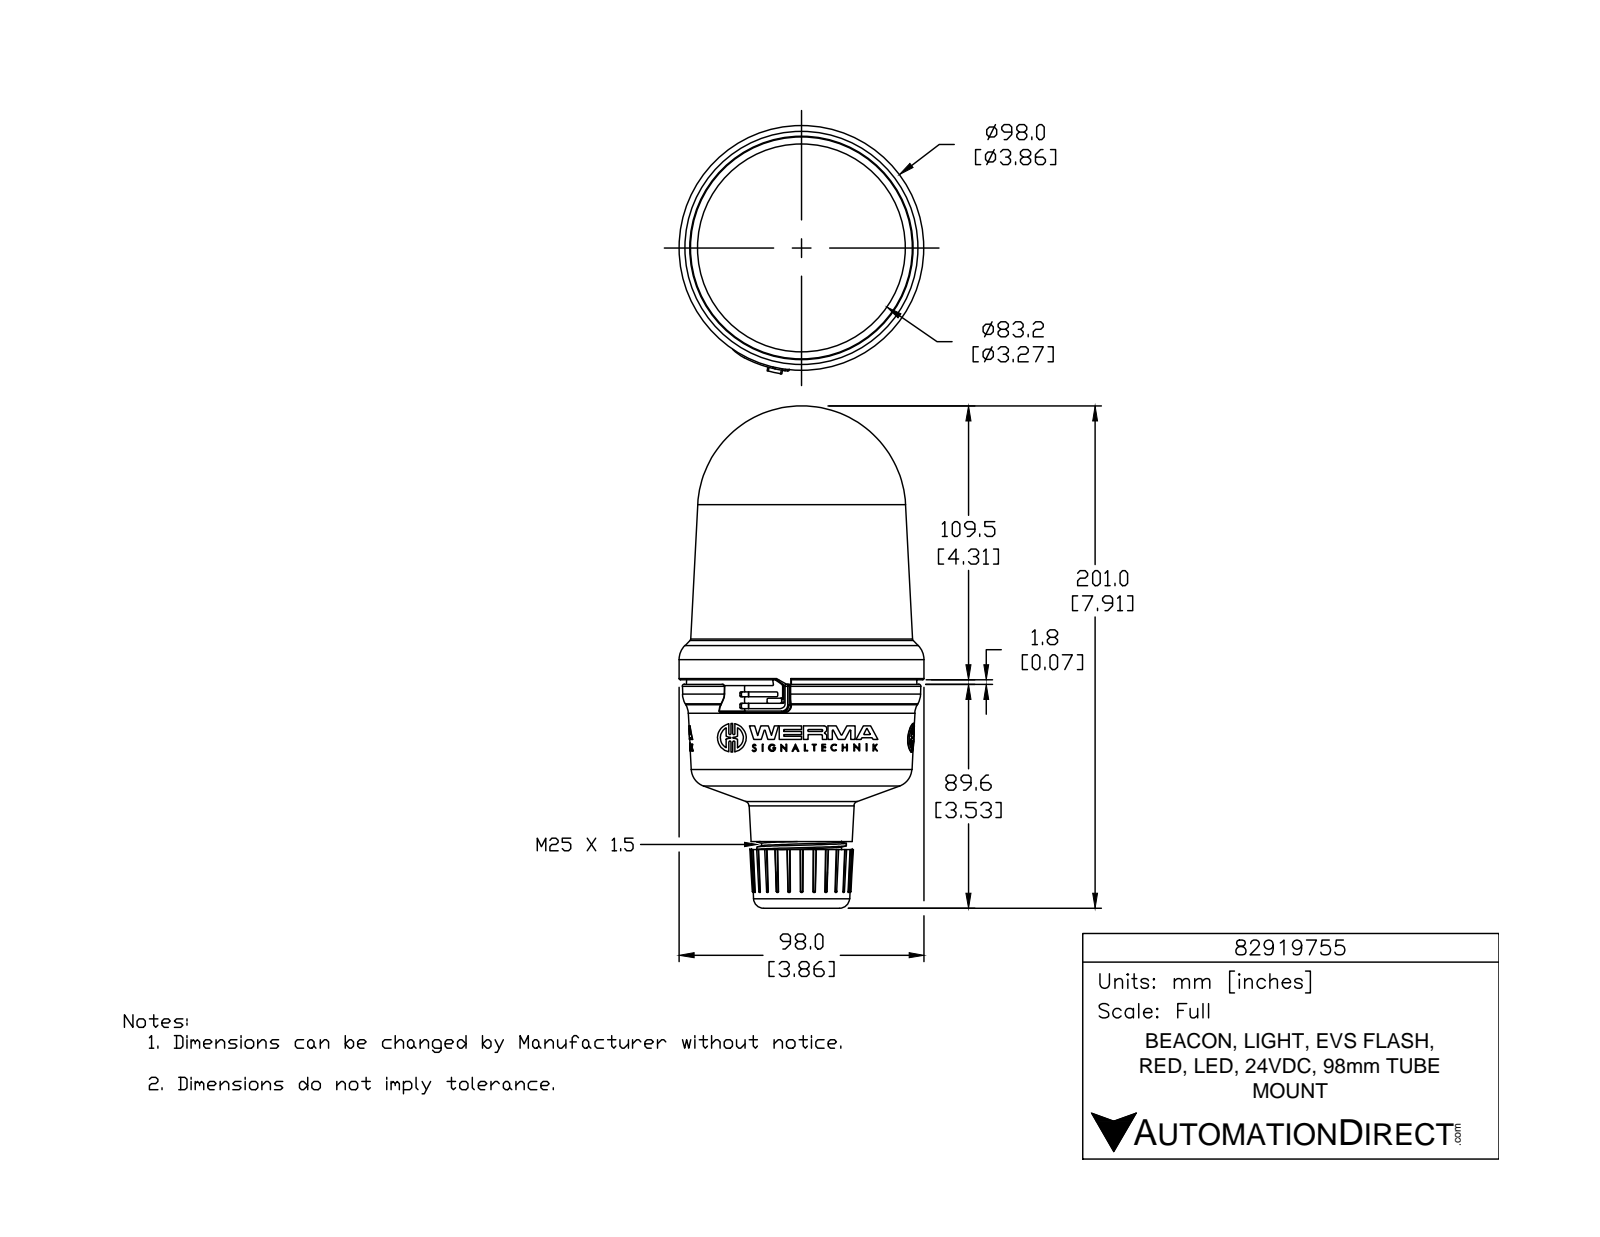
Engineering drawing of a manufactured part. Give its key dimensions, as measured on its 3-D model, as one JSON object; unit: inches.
{"part_name": "82919755", "step_written_by": "SolidWorks 2015 (AUTOMOTIVE_DESIGN)", "units": "inches", "bodies": {"solids": 1, "faces": 1006, "planar": 554, "cylindrical": 189, "other": 263}, "overall_size": [7.914, 3.912, 3.858], "volume_in3": 54.7, "surface_area_in2": 91.39, "round_holes": [[0.078, 3], [1.013, 1], [1.024, 1]], "round_bosses_or_shafts": [[0.452, 3], [0.113, 3], [3.858, 1], [1.409, 1], [1.261, 1]], "partial_cylinders_radius": [[0.02, 12], [0.007, 9], [0.007, 6], [0.016, 6], [0.016, 6], [0.016, 6], [0.262, 6], [0.006, 3]], "face_to_face_distances": [2.214, 0.462, 2.676, 0.335, 0.127, 2.548, 2.603, 2.476, 2.141, 0.073]}
